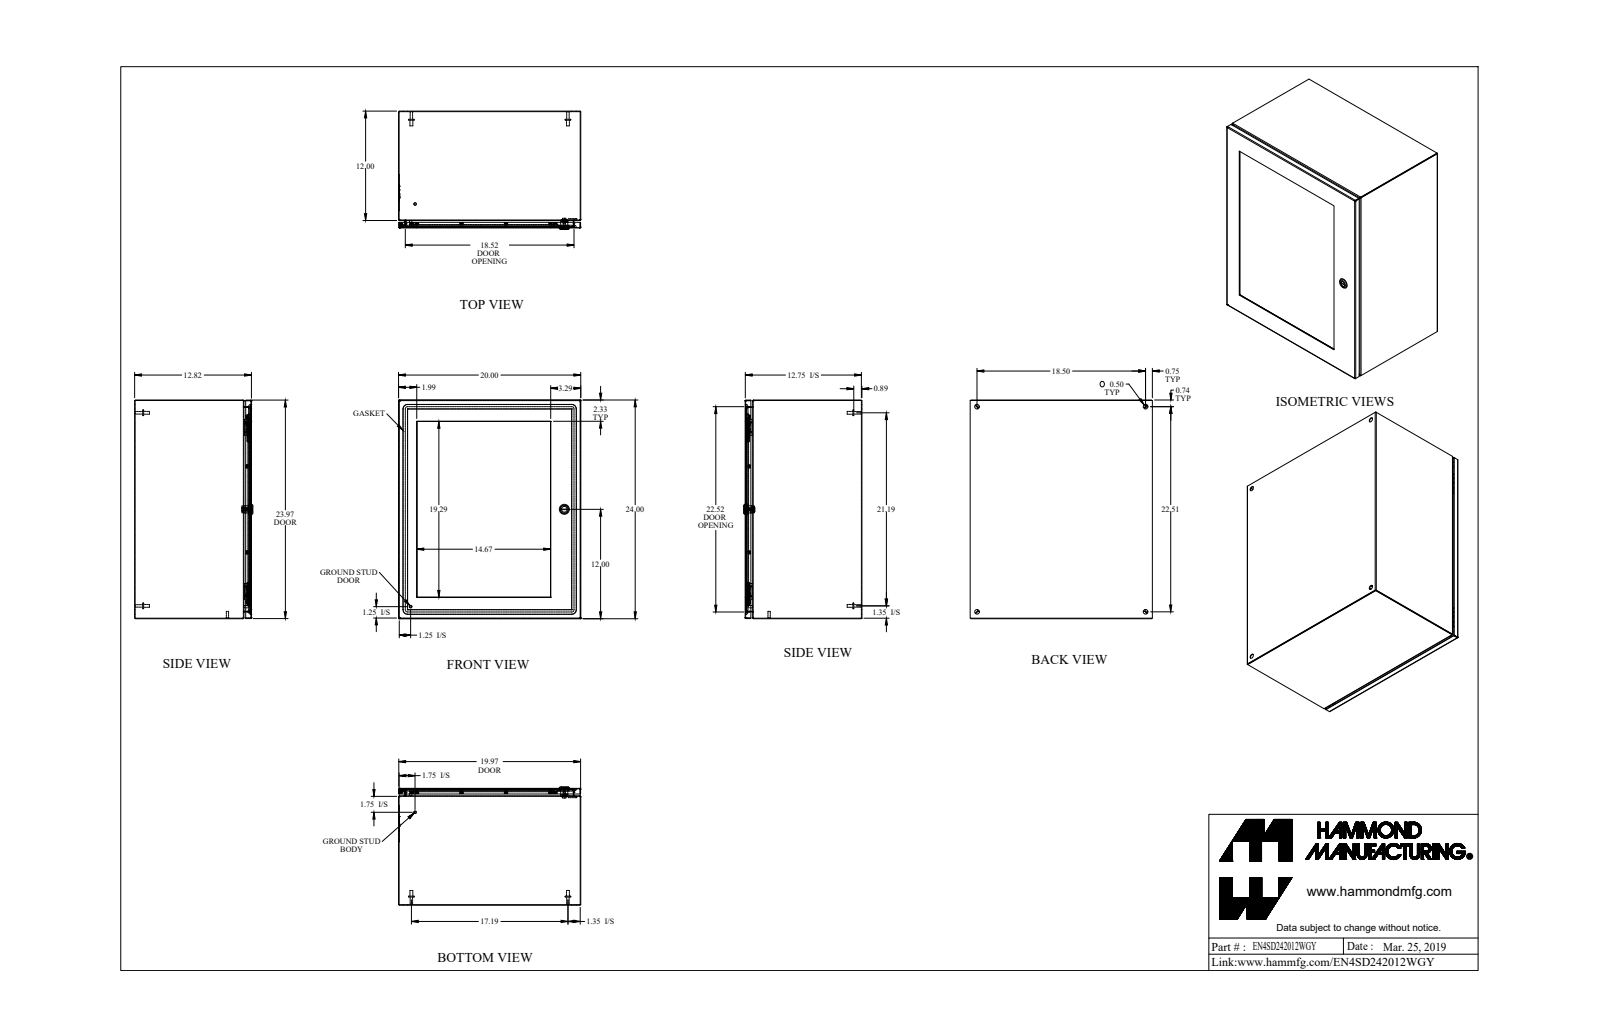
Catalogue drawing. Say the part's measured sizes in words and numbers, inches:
The part is named "EN4SD242012WGY". Its 3-D file was written by "SolidWorks 2019 (AUTOMOTIVE_DESIGN)". It is 70 solids with 1340 faces: 671 planar, 405 cylindrical and 264 other. Overall it measures 24 by 20 by 12.982 inches. Its volume is 202.3 cubic inches and its surface area 4 853 square inches. Round holes: 18 of diameter 0.13, 18 of diameter 0.25, 4 of diameter 0.5, 1 of diameter 0.172, 1 of diameter 0.232, 1 of diameter 0.24, 1 of diameter 0.242, 1 of diameter 0.625, 1 of diameter 0.785. Round bosses or shafts: 19 of diameter 0.226, 18 of diameter 0.368, 18 of diameter 0.164, 4 of diameter 0.625, 4 of diameter 0.313, 4 of diameter 0.27, 2 of diameter 0.281, 2 of diameter 0.25. Partial cylindrical surfaces (rounded edges, fillets, slot ends): 15 of radius 0.029, 15 of radius 0.086, 12 of radius 0.188, 10 of radius 0.125, 8 of radius 0.1, 4 of radius 0.006, 4 of radius 0.016, 4 of radius 0.062. The main face-to-face distances are 0.057, 19.943, 12.765, 23.943, 12.708, 0.25, 12.458, 12.515, 0.072, 19.886. The hole center spacings are 4.719, 9.437, 14.156, 16.403, 5.472, 14.894, 16.4, 18.324.
